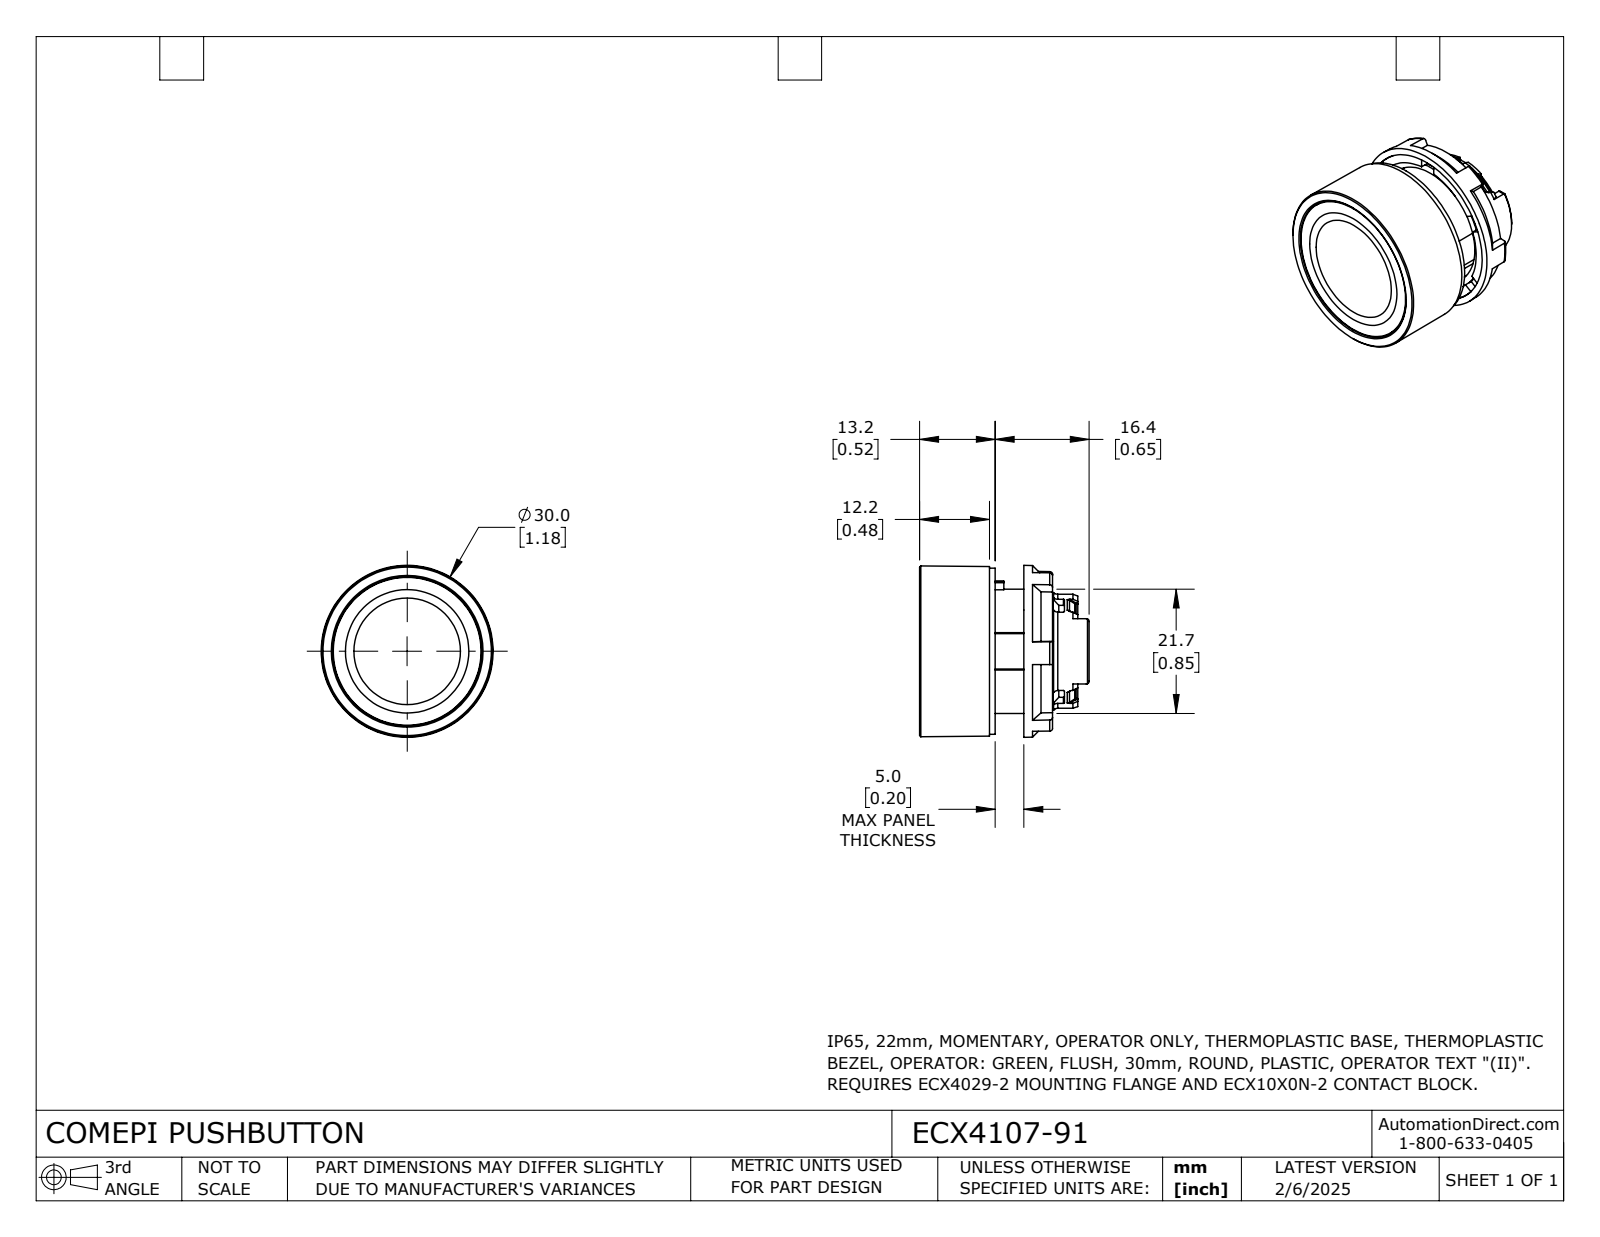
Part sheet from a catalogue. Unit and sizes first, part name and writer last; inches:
Units: inches
Overall size (bounding box): 1.181 × 1.181 × 1.165
Round holes (diameter × count): ⌀0.531 ×1, ⌀0.713 ×1, ⌀0.866 ×1
Round bosses / shafts (diameter × count): ⌀1.142 ×1, ⌀1.016 ×1, ⌀0.965 ×1, ⌀0.854 ×1, ⌀0.807 ×1, ⌀0.787 ×1, ⌀0.748 ×1, ⌀0.728 ×1
Partial cylindrical surfaces — rounded edges, fillets, slot ends (radius × count): R0.008 ×24, R0.02 ×8, R0.01 ×2, R0.293 ×1, R0.344 ×1, R0.348 ×1, R0.366 ×1
Main face-to-face distances: 0.409, 0.039, 0.433, 0.472, 0.236, 0.394, 0.197, 0.449, 0.512, 0.217
Volume: 0.472 in³ · Surface area: 16.55 in²
Bodies: 3 solids, 398 faces (134 planar, 111 cylindrical, 153 other)
Part name (STEP PRODUCT): ECX4107-91
STEP written by: SolidWorks 2024 (CONFIG_CONTROL_DESIGN)
